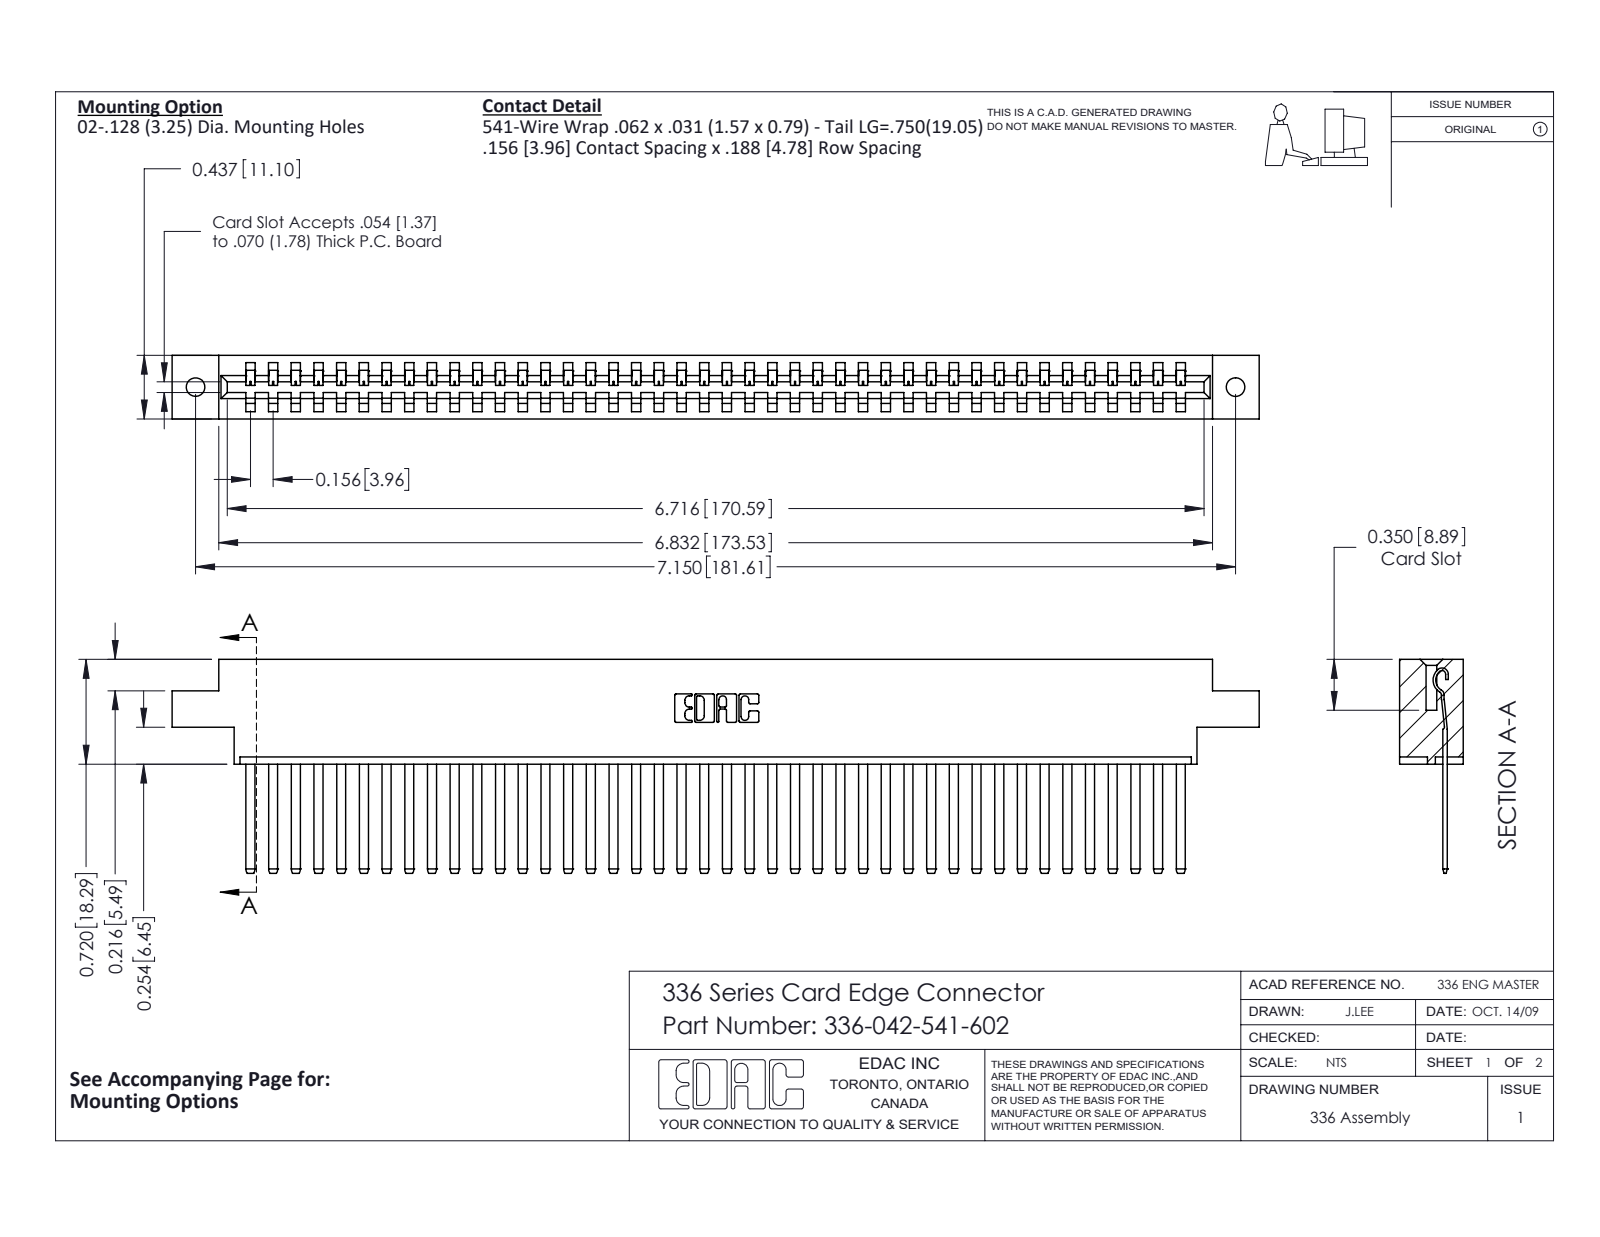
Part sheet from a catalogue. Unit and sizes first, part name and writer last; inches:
Units: inches
Overall size (bounding box): 7.473 × 1.47 × 0.437
Round holes (diameter × count): ⌀0.128 ×2
Partial cylindrical surfaces — rounded edges, fillets, slot ends (radius × count): R0.004 ×84, R0.056 ×84, R0.01 ×22, R0.007 ×6, R0.031 ×6, R0.026 ×3, R0.022 ×2, R0.04 ×2
Main face-to-face distances: 0.437, 0.181, 0.328, 0.14, 0.297, 0.109, 0.031, 0.256, 0.05, 0.387
Hole centre spacings: 7.15
Volume: 1.677 in³ · Surface area: 46.22 in²
Bodies: 43 solids, 2218 faces (1502 planar, 716 cylindrical, 0 other)
Part name (STEP PRODUCT): 336-042-541-602; 336 Part_Offset - .128 Dia; 336-290-001_336-290-541
STEP written by: SolidWorks 2020 (CONFIG_CONTROL_DESIGN)
